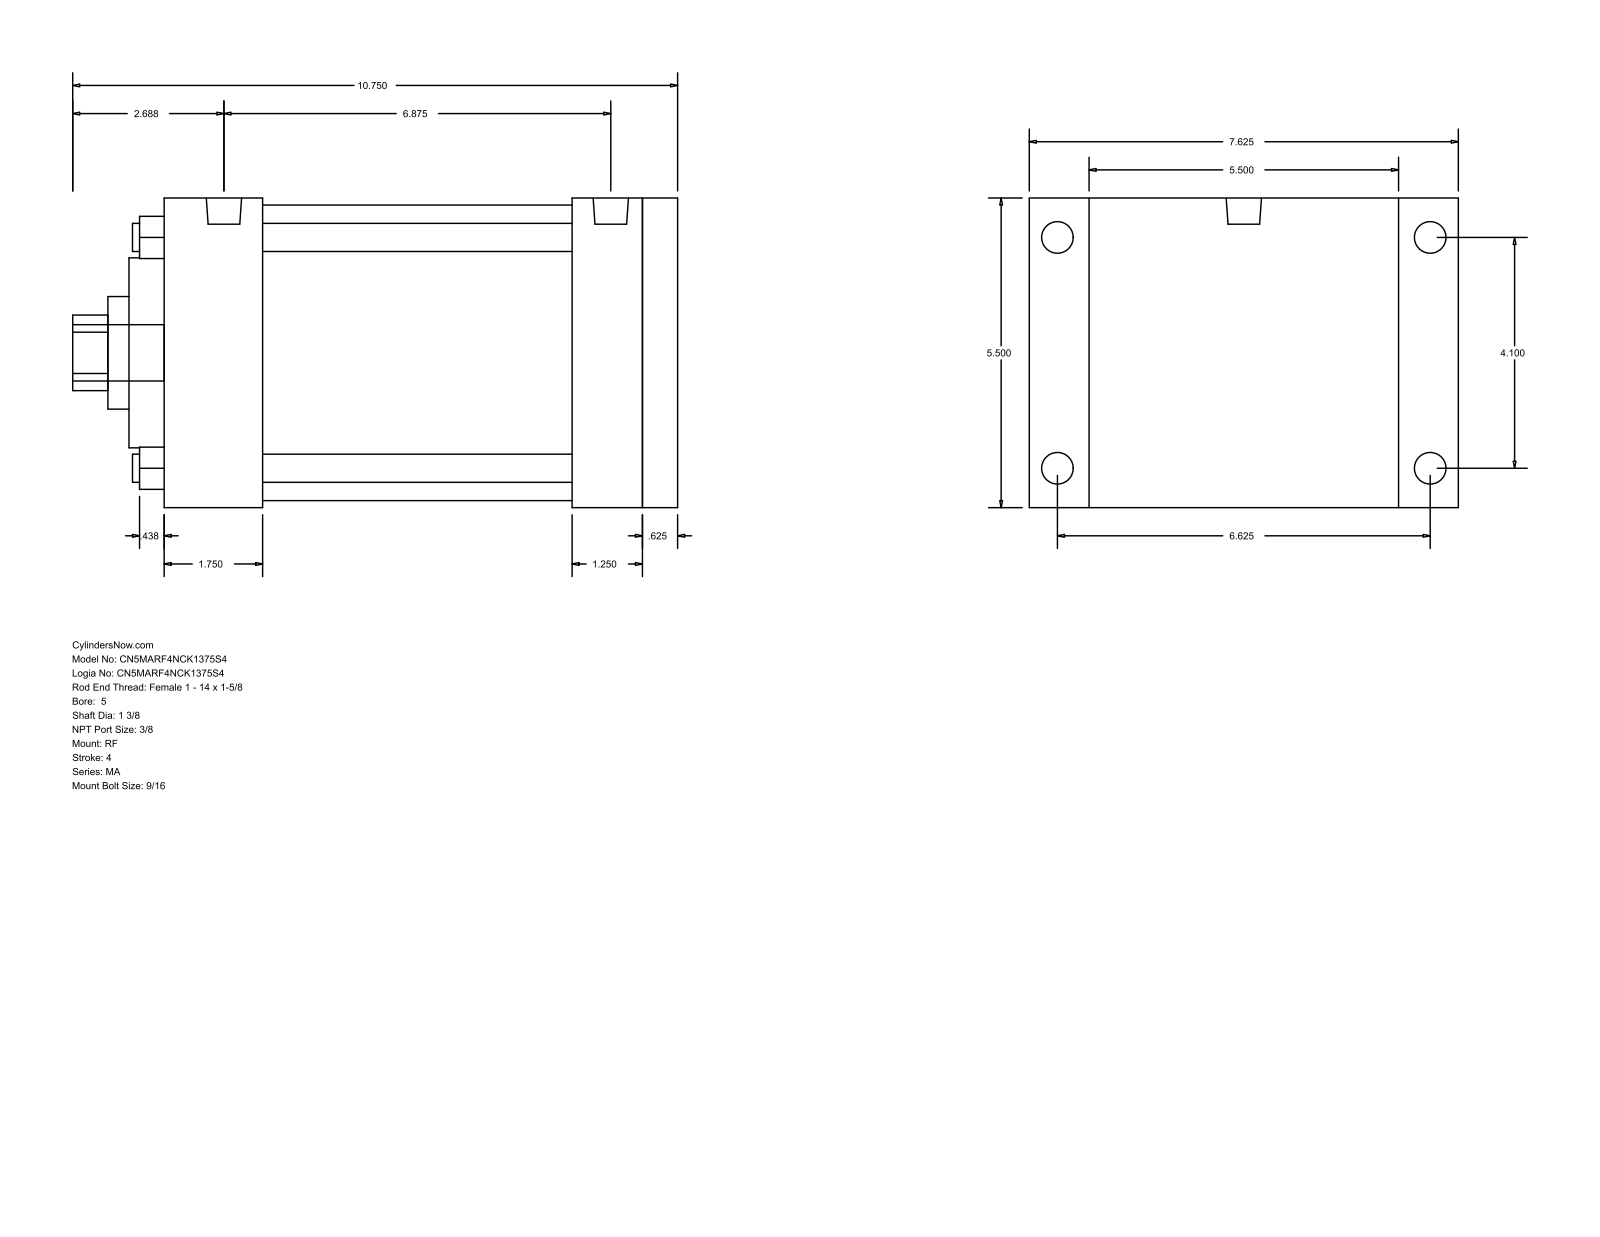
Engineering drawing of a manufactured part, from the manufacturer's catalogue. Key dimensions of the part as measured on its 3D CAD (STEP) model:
Part name (STEP PRODUCT): MA_RF__0500_1.375
STEP written by: GSSL Pune (CONFIG_CONTROL_DESIGN)
Units: millimetres
Bodies: 0 solids, 94 faces (65 planar, 29 cylindrical, 0 other)
Overall size (bounding box): 273.05 × 193.68 × 139.7
Round holes (diameter × count): ⌀12.7 ×4, ⌀34.92 ×1, ⌀50.8 ×1, ⌀85.72 ×1, ⌀133.35 ×1
Round bosses / shafts (diameter × count): ⌀14.29 ×4, ⌀11.11 ×4, ⌀15.93 ×2, ⌀25.4 ×1
Partial cylindrical surfaces — rounded edges, fillets, slot ends (radius × count): R17.06 ×1
Main face-to-face distances: 139.7, 231.78, 15.87, 215.91, 44.45, 171.46, 187.33, 184.16, 139.71, 31.75
Hole centre spacings: 73.64, 104.14, 147.28
